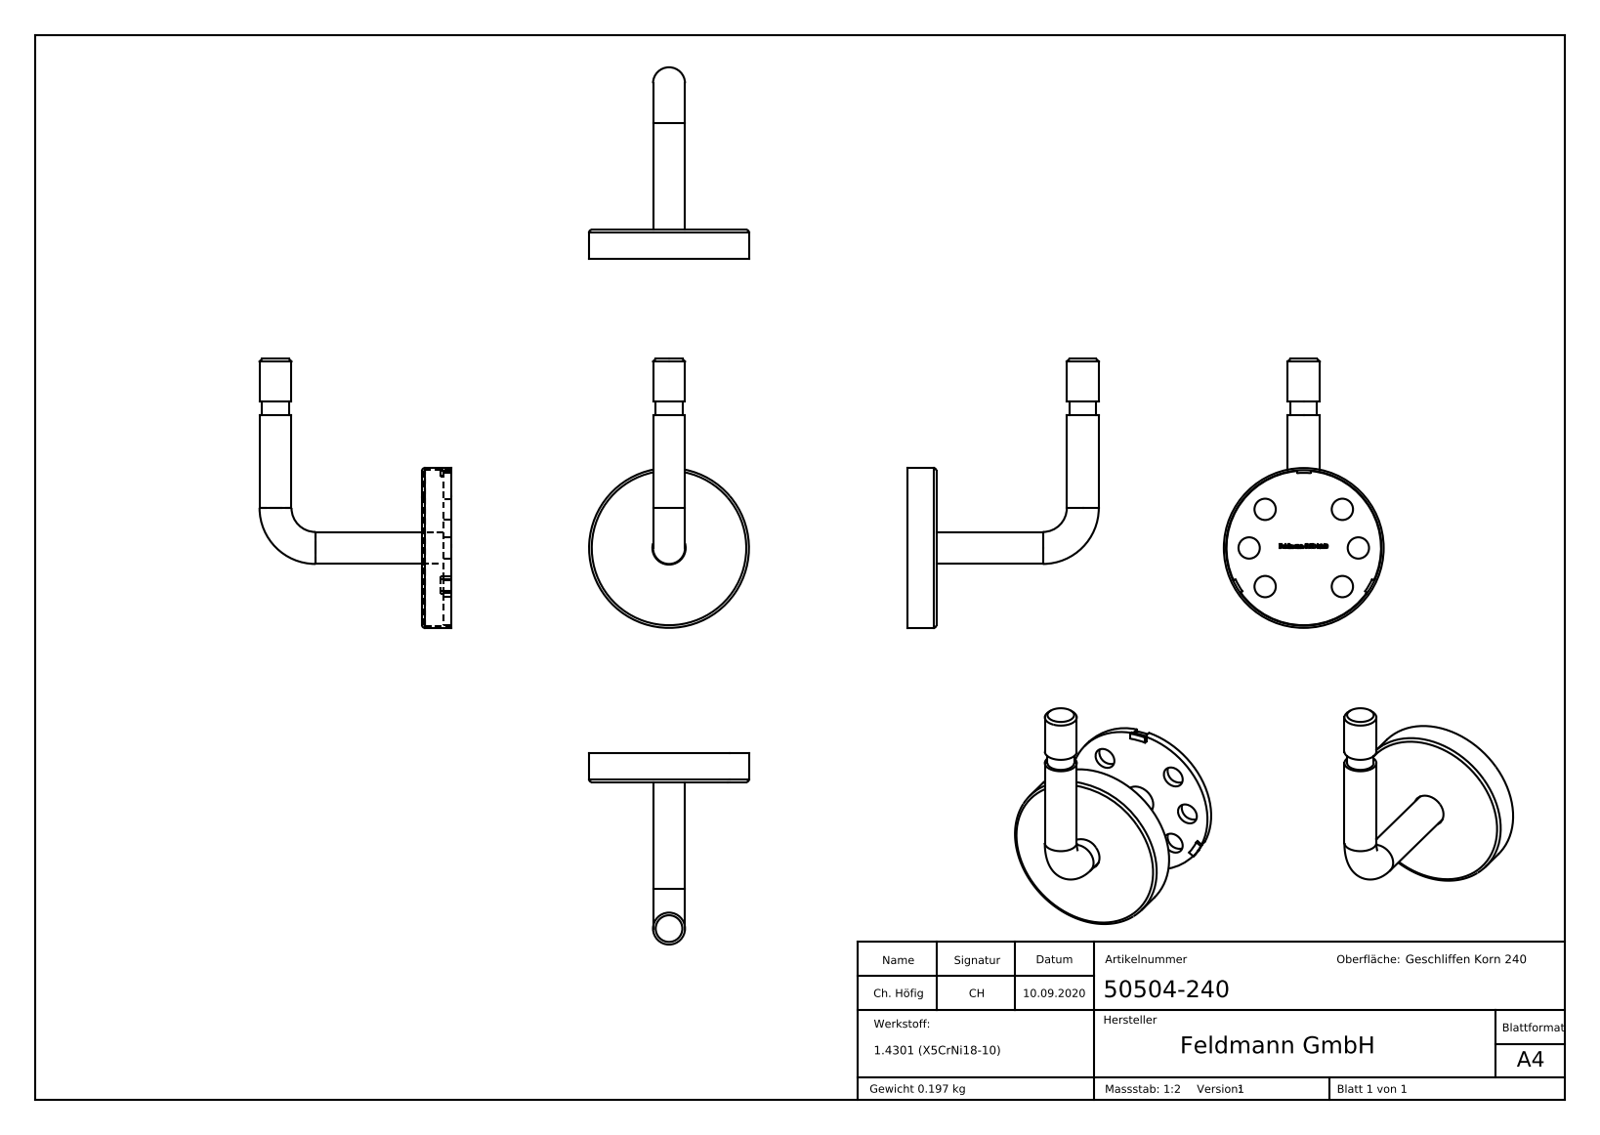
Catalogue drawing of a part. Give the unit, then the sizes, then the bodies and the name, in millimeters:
Units: millimetres
Overall size (bounding box): 101 × 72 × 60
Round holes (diameter × count): ⌀8 ×6, ⌀12.5 ×1
Round bosses / shafts (diameter × count): ⌀12 ×2, ⌀60 ×1, ⌀58.4 ×1, ⌀58 ×1, ⌀10 ×1
Partial cylindrical surfaces — rounded edges, fillets, slot ends (radius × count): R27 ×1, R28.2 ×1
Main face-to-face distances: 0.8, 10.2, 11, 3, 7.2, 8, 6.2, 4, 1, 7
Hole centre spacings: 15.69, 20.51, 29, 37.88, 20.5, 41.01, 41
Volume: 24 904 mm³ · Surface area: 19 874 mm²
Bodies: 2 solids, 297 faces (153 planar, 39 cylindrical, 105 other)
Part name (STEP PRODUCT): 50504-240 Teil1_50504-240 Teil1; 50504-240; 50504-240 Teil2_50504-240 Teil2; 50504-240 Teil1 (+1 more)
STEP written by: SolidWorks 2018 (CONFIG_CONTROL_DESIGN)
